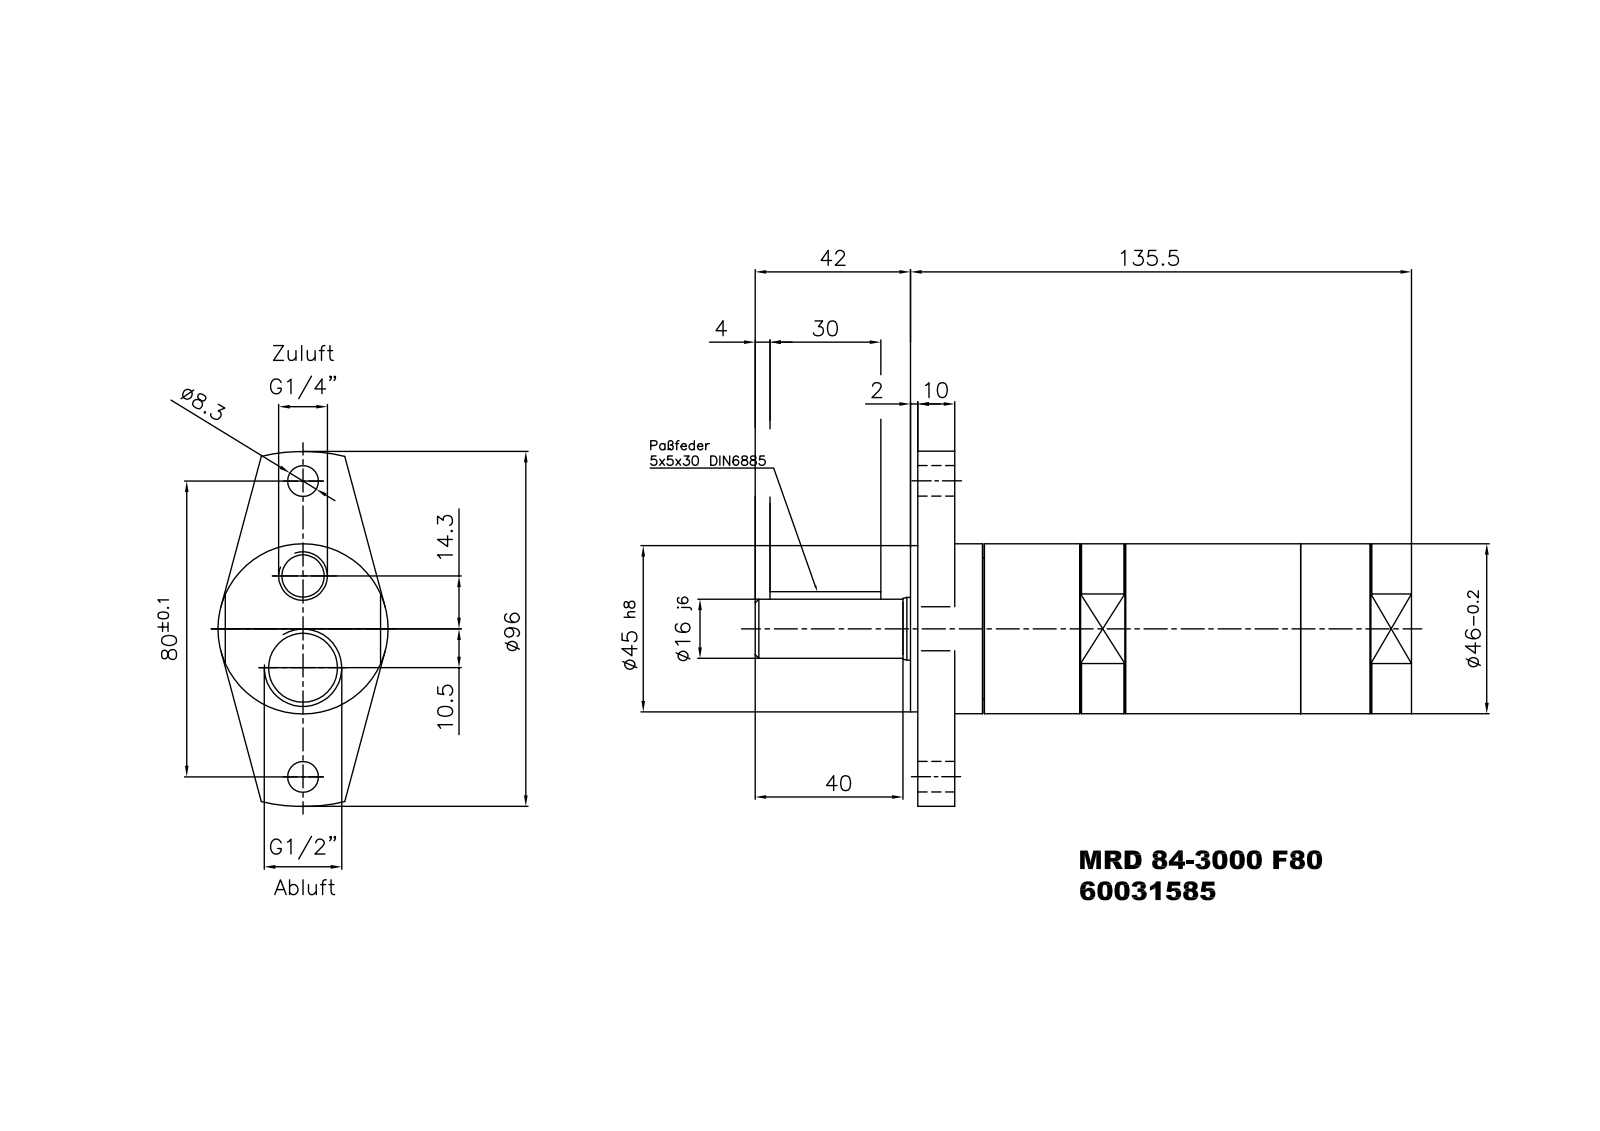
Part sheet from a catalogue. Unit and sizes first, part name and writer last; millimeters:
Units: millimetres
Overall size (bounding box): 177.5 × 96 × 46
Round holes (diameter × count): ⌀8.3 ×2, ⌀1.6 ×1, ⌀11.45 ×1, ⌀17.5 ×1, ⌀18.63 ×1
Round bosses / shafts (diameter × count): ⌀46 ×1, ⌀45 ×1, ⌀40 ×1, ⌀16.95 ×1, ⌀16 ×1
Partial cylindrical surfaces — rounded edges, fillets, slot ends (radius × count): R2.5 ×2, R48 ×1
Main face-to-face distances: 103.5, 10, 93.5, 12, 2, 105.5, 123.5, 135.5, 133.5, 30
Hole centre spacings: 40, 10.5, 14.3, 24.8, 25.7, 29.5, 50.5, 54.3
Volume: 242 672 mm³ · Surface area: 35 804 mm²
Bodies: 2 solids, 147 faces (93 planar, 22 cylindrical, 32 other)
Part name (STEP PRODUCT): MRD 84-10800 3000 2370 1350 F80 177,5mm
STEP written by: Autodesk Inventor 2013 (AUTOMOTIVE_DESIGN)
